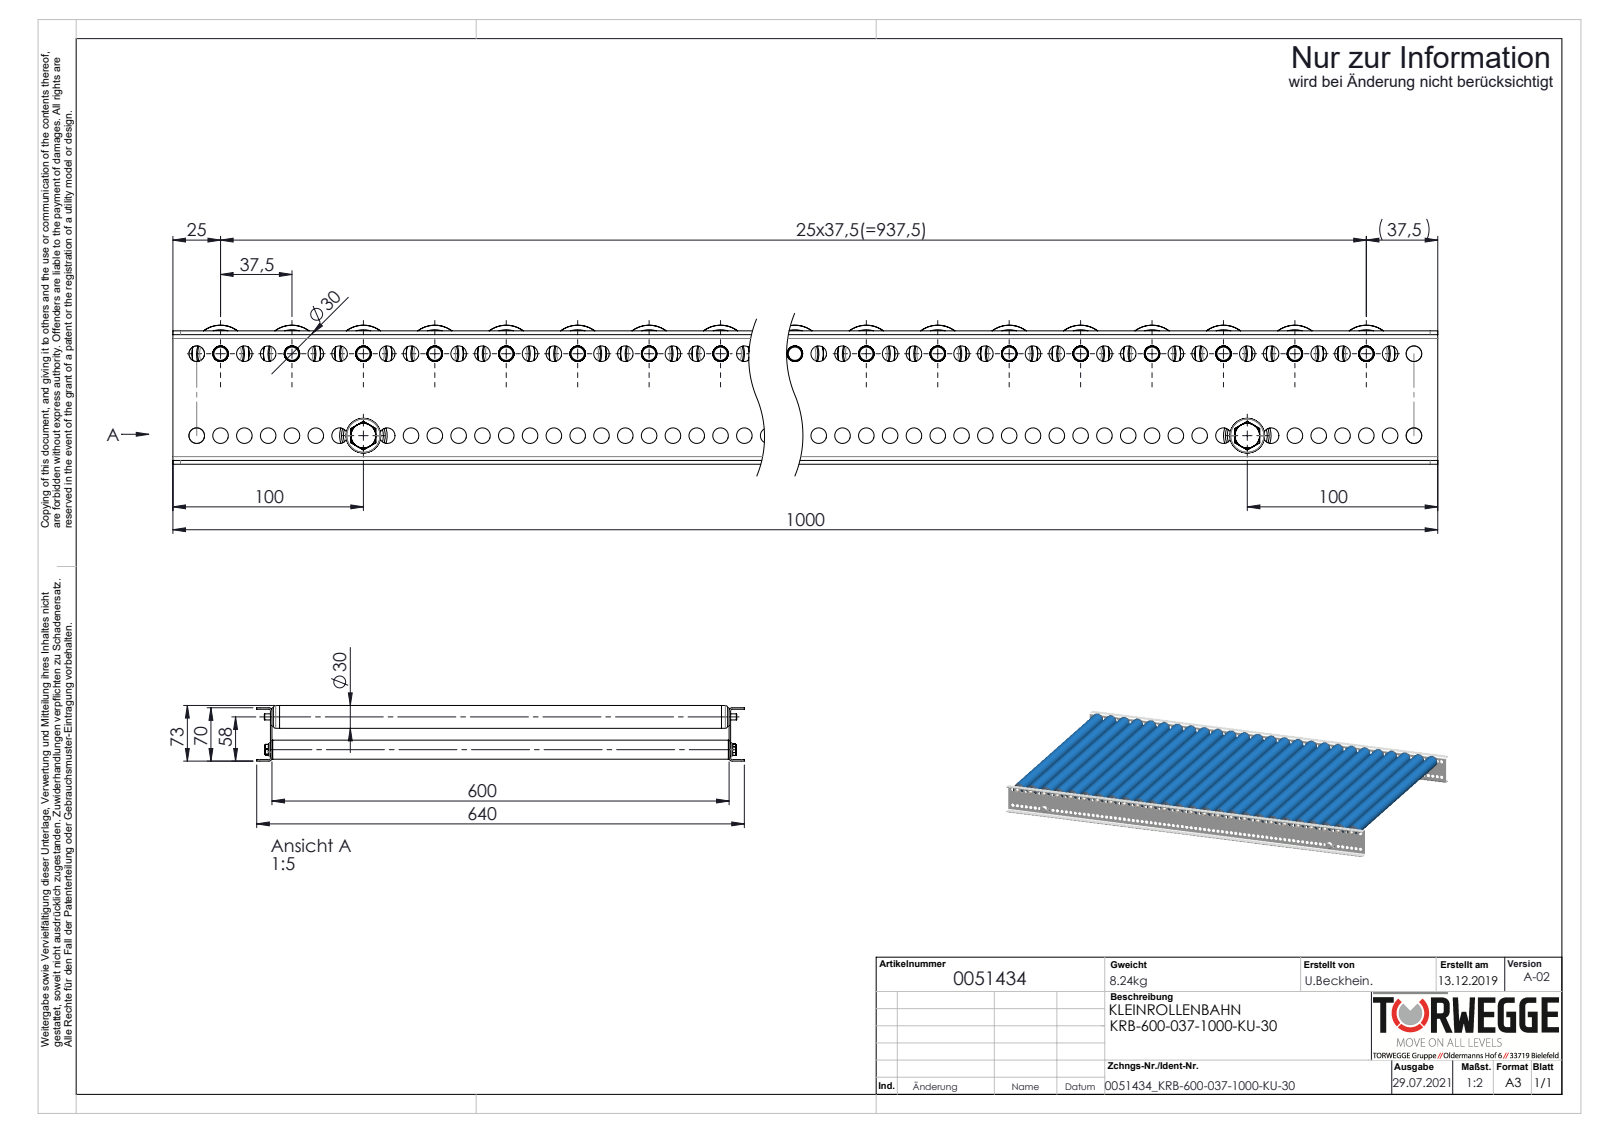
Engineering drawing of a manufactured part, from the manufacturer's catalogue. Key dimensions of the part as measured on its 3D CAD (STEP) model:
Part name (STEP PRODUCT): S100994_Sperrzahnschraube_M08x16-8.8-A2K; 0017013_Tragrollenrohr-Ø30x1,8KU_KFG_L=580; 0039778-Achse-ST-Ø08-KFG_AL620-G-FA; Profil_KRB-20x70x20x2_KFG_S100230_U-PROFIL-20-70-20-2-KRB-30-L=1000 (+4 more)
STEP written by: SolidWorks 2020 (AUTOMOTIVE_DESIGN)
Units: millimetres
Bodies: 64 solids, 6268 faces (1940 planar, 2352 cylindrical, 1976 other)
Overall size (bounding box): 1000 × 640 × 73
Volume: 3 796 000 mm³ · Surface area: 3 982 000 mm²
Round holes (diameter × count): ⌀8.2 ×158, ⌀8.1 ×26, ⌀22.6 ×26, ⌀25.2 ×26, ⌀6.8 ×2, ⌀21 ×2
Round bosses / shafts (diameter × count): ⌀8 ×28, ⌀30 ×26, ⌀29.9 ×26, ⌀26.5 ×26, ⌀26.4 ×26, ⌀24 ×26, ⌀25 ×2
Partial cylindrical surfaces — rounded edges, fillets, slot ends (radius × count): R5.05 ×26, R4 ×8, R2 ×4
Main face-to-face distances: 2, 602, 68, 600, 604, 66, 70, 10, 590, 12
Hole centre spacings: 12.5, 25, 37.5, 50, 62.5, 75, 87.5, 100
